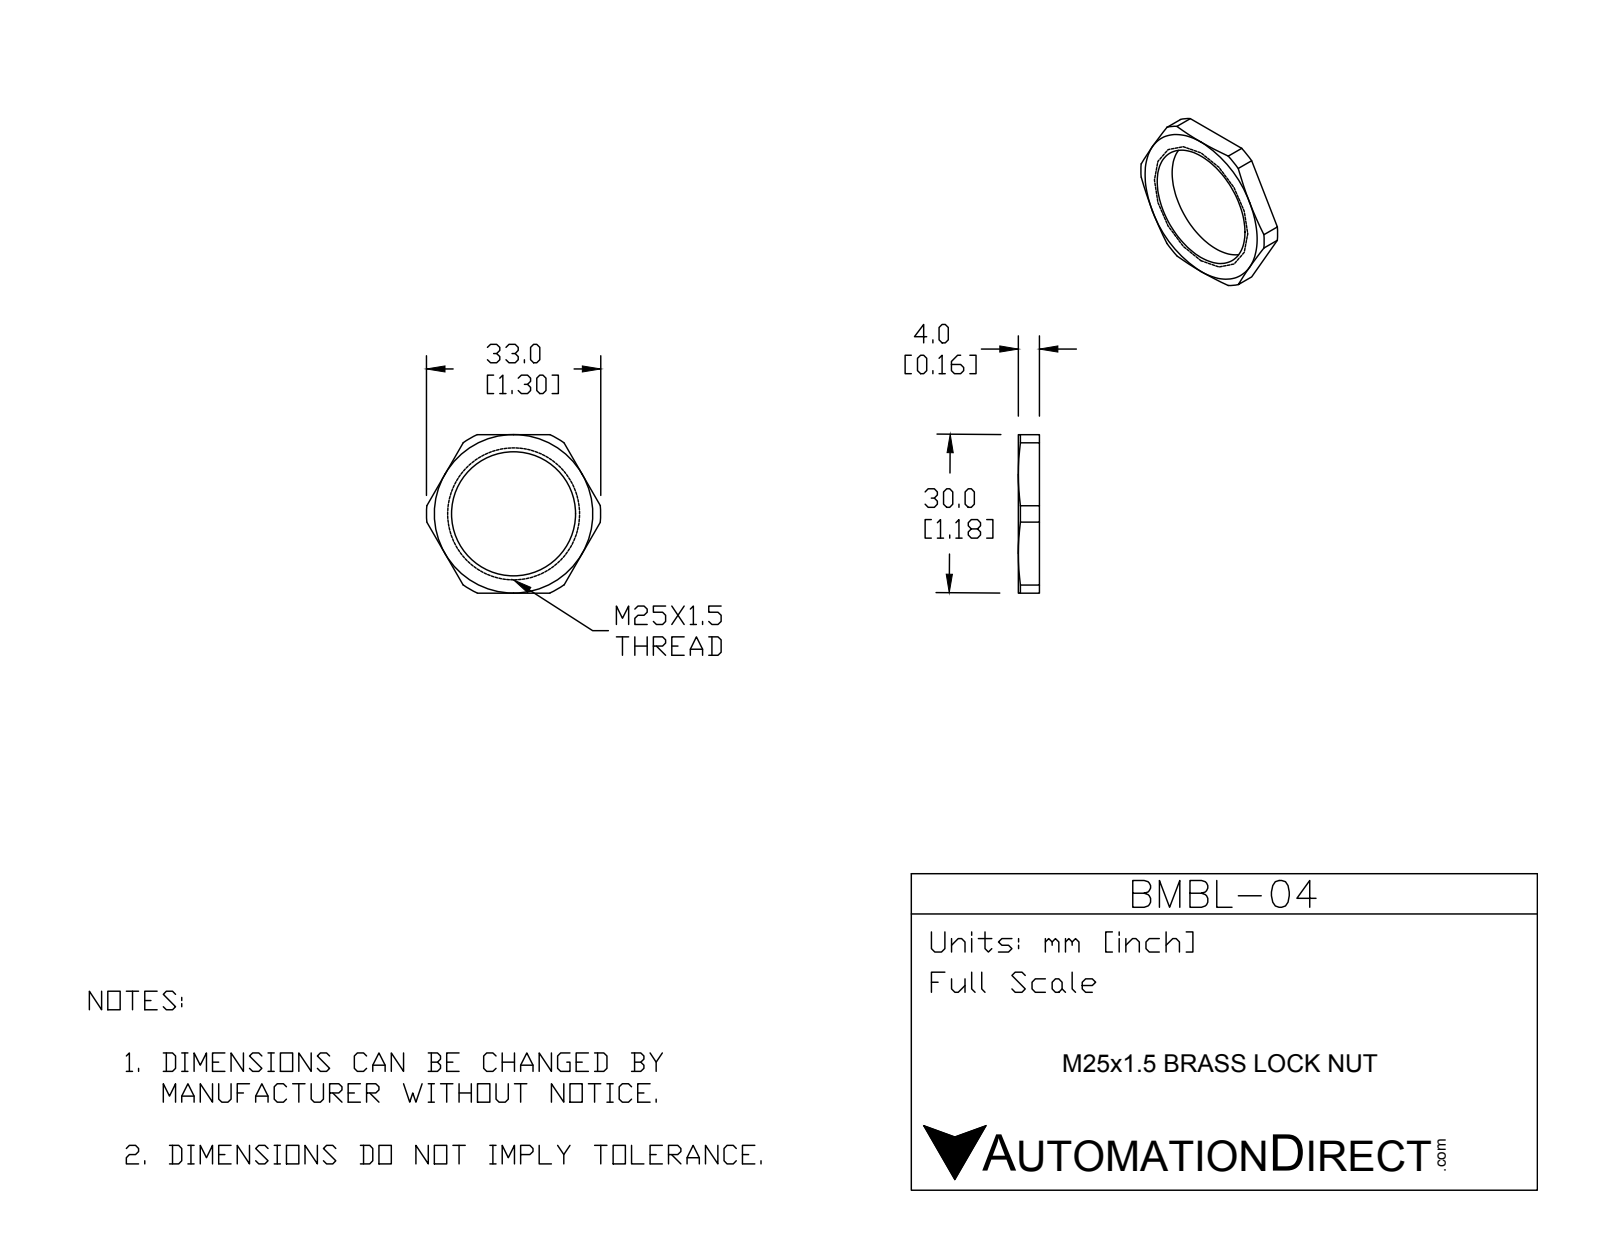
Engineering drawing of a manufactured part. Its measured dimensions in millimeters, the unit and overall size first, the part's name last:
Units: millimetres
Overall size (bounding box): 33 × 30 × 4
Round holes (diameter × count): ⌀23.5 ×1
Partial cylindrical surfaces — rounded edges, fillets, slot ends (radius × count): R16.5 ×1
Main face-to-face distances: 4, 30
Volume: 1 343 mm³ · Surface area: 1 360 mm²
Bodies: 1 solid, 23 faces (8 planar, 9 cylindrical, 6 other)
Part name (STEP PRODUCT): BMBL-04
STEP written by: SolidWorks 2015 (CONFIG_CONTROL_DESIGN)
